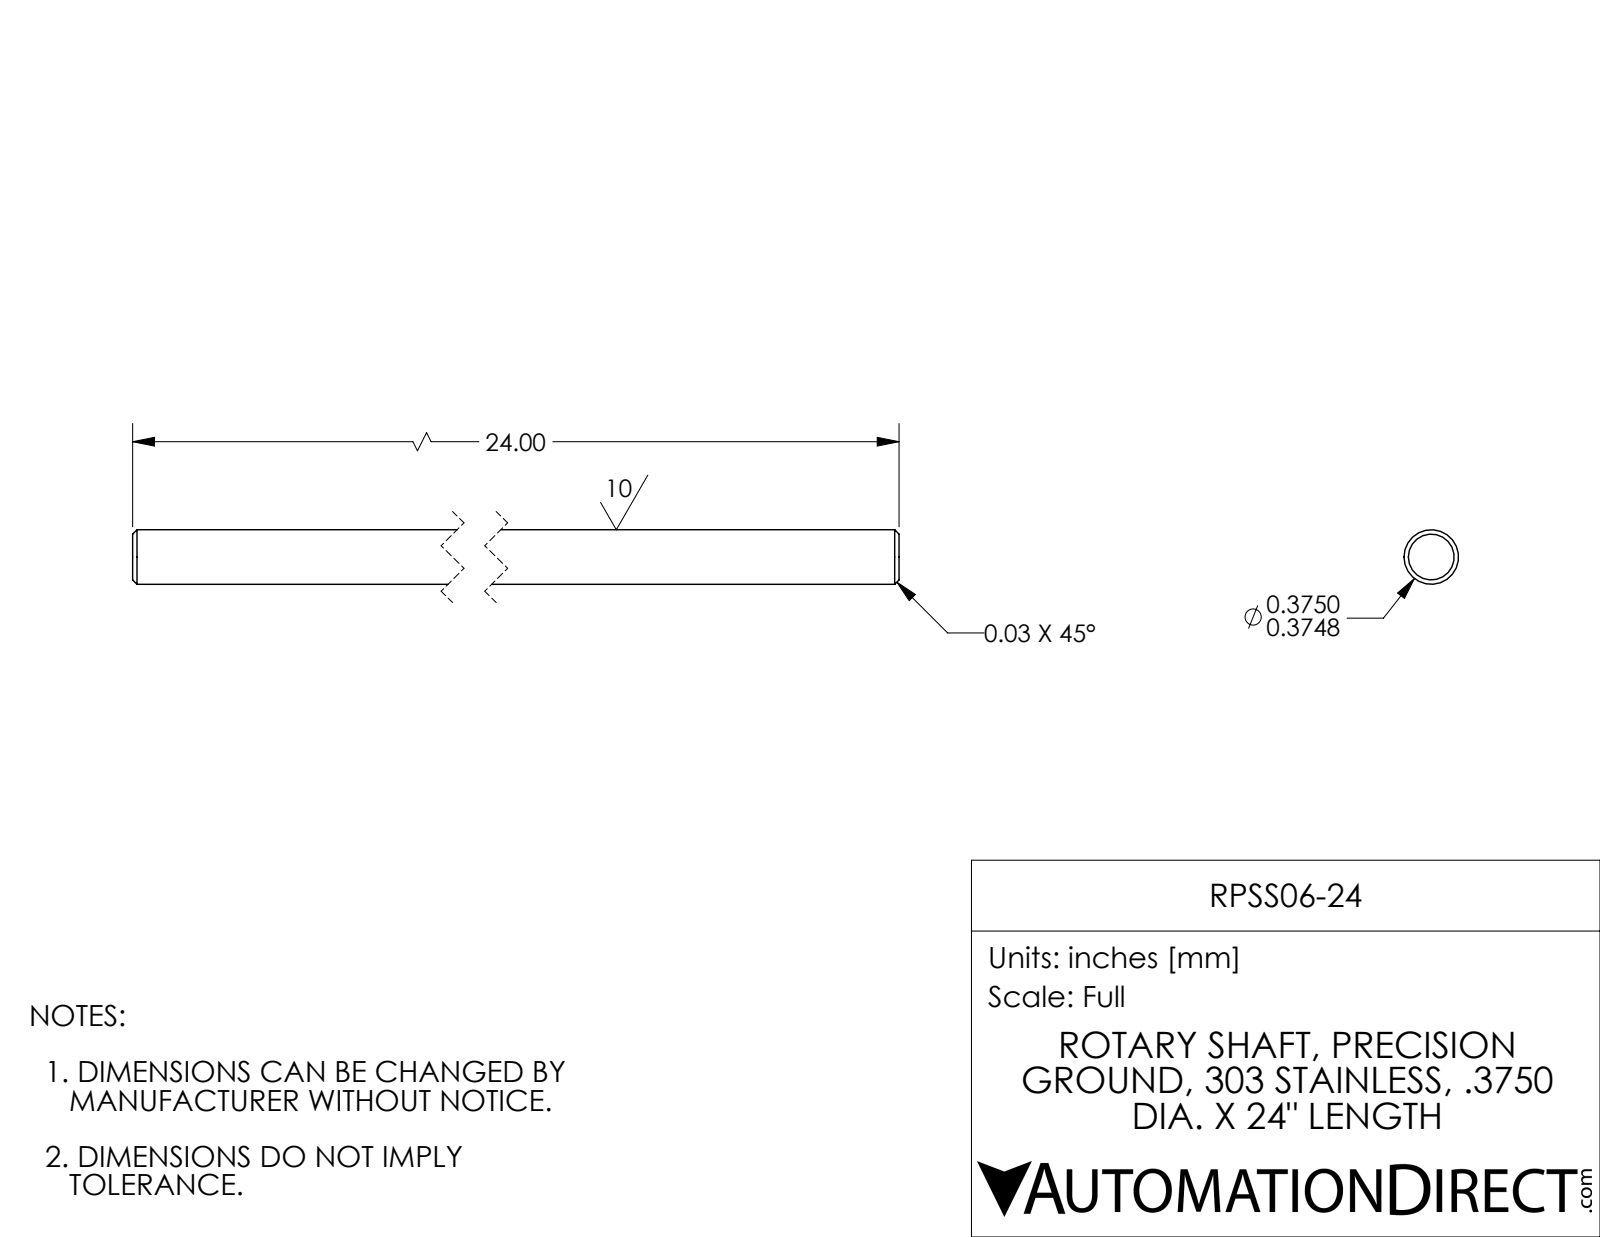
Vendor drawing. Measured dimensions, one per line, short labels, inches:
name: RPSS06-24
written by: SolidWorks 2017 (AUTOMOTIVE_DESIGN)
unit: in
bodies: 1 solid, 8 faces (2 planar, 2 cylindrical, 4 other)
size: 24 × 0.375 × 0.375
volume: 2.65 in³; area: 28.45 in²
bosses: 1× ⌀0.375
face distances: 24
